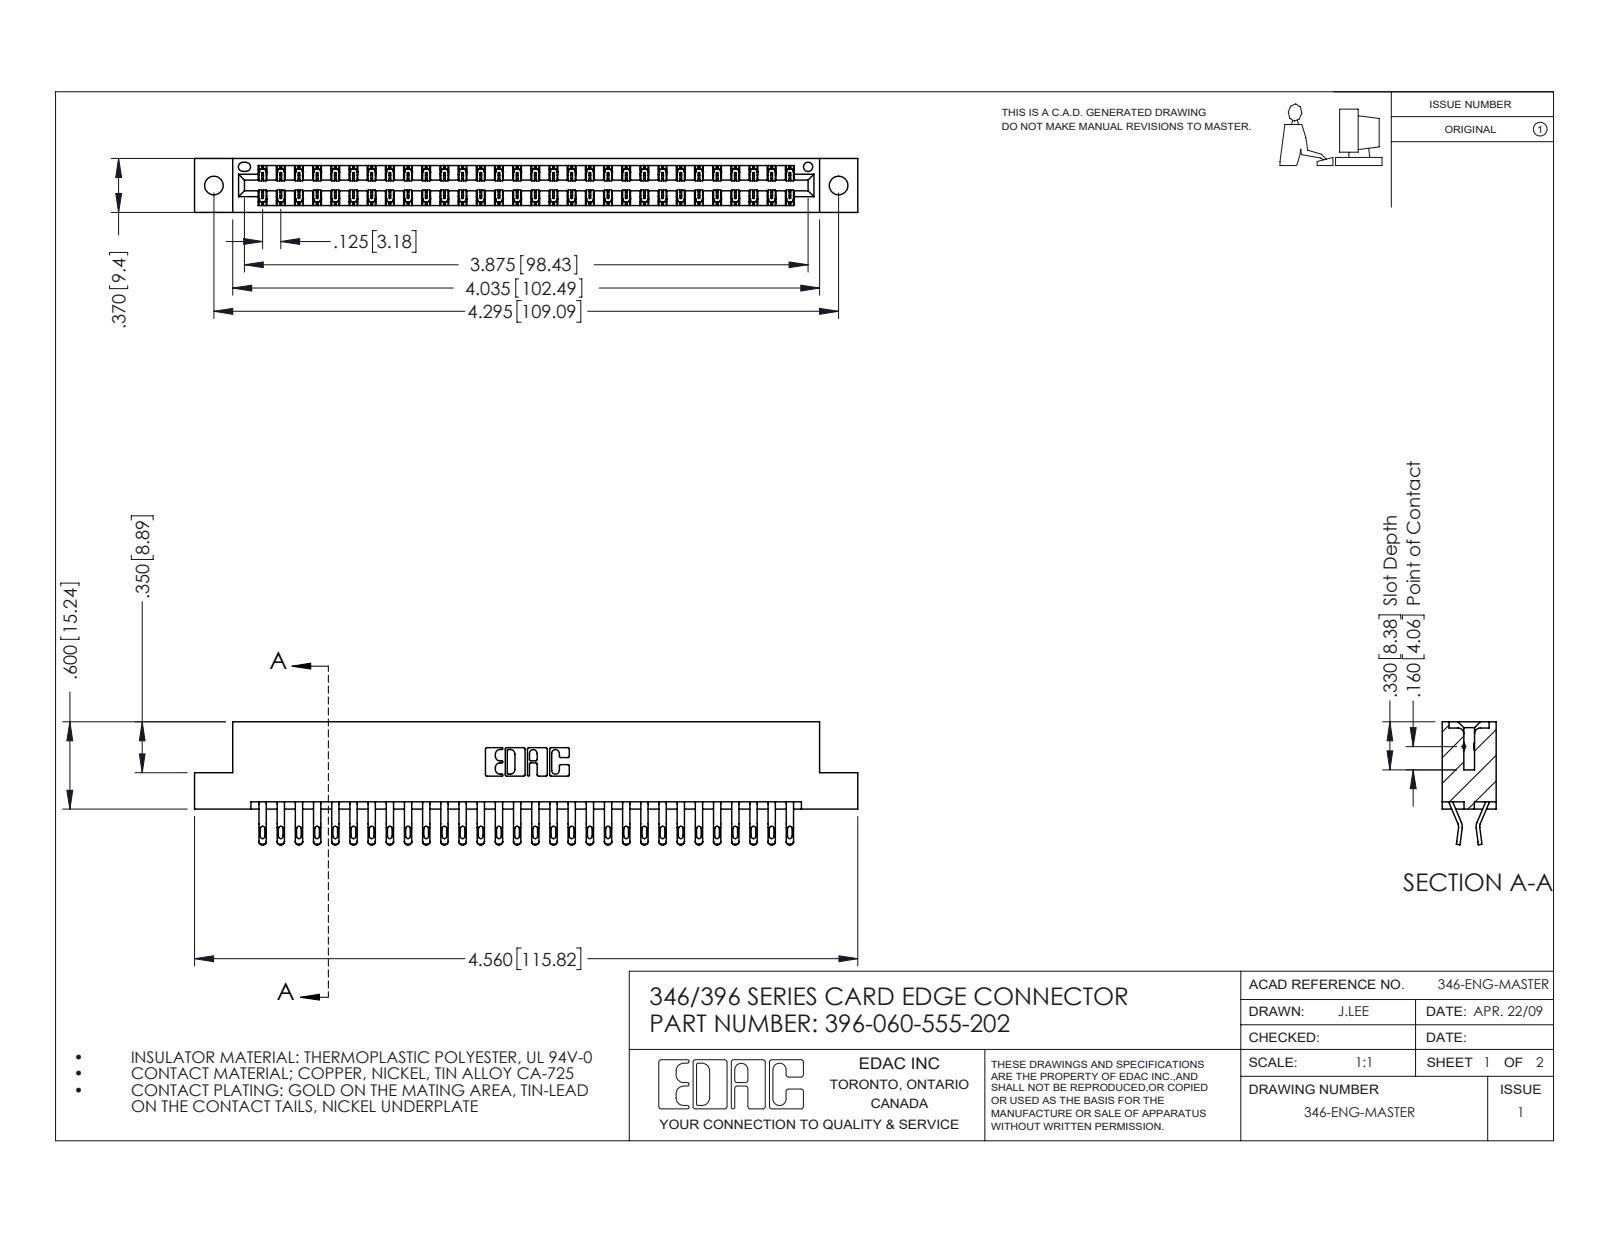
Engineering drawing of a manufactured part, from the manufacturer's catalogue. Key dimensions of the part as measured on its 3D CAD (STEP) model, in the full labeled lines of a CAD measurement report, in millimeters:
Part name (STEP PRODUCT): 346 Part_Flush Mounting Lugs - 0.128 Dia; 396-060-555-202; 345-292-001_555 Tail
STEP written by: SolidWorks 2016 (CONFIG_CONTROL_DESIGN)
Units: millimetres
Bodies: 61 solids, 3602 faces (2056 planar, 1546 cylindrical, 0 other)
Overall size (bounding box): 115.8 × 21.5 × 9.4
Volume: 11 300 mm³ · Surface area: 15 750 mm²
Round holes (diameter × count): ⌀3.3 ×2, ⌀1.6 ×1
Partial cylindrical surfaces — rounded edges, fillets, slot ends (radius × count): R0.4 ×120, R0.5 ×120, R0.2 ×90, R0.3 ×22, R0.2 ×6, R0.8 ×6, R0.7 ×3, R0.3 ×2
Main face-to-face distances: 1.2, 8.2, 9.4, 6.4, 0.6, 1.8, 7.6, 7, 3.8, 5.6
Hole centre spacings: 6.2, 103.8, 109.1
